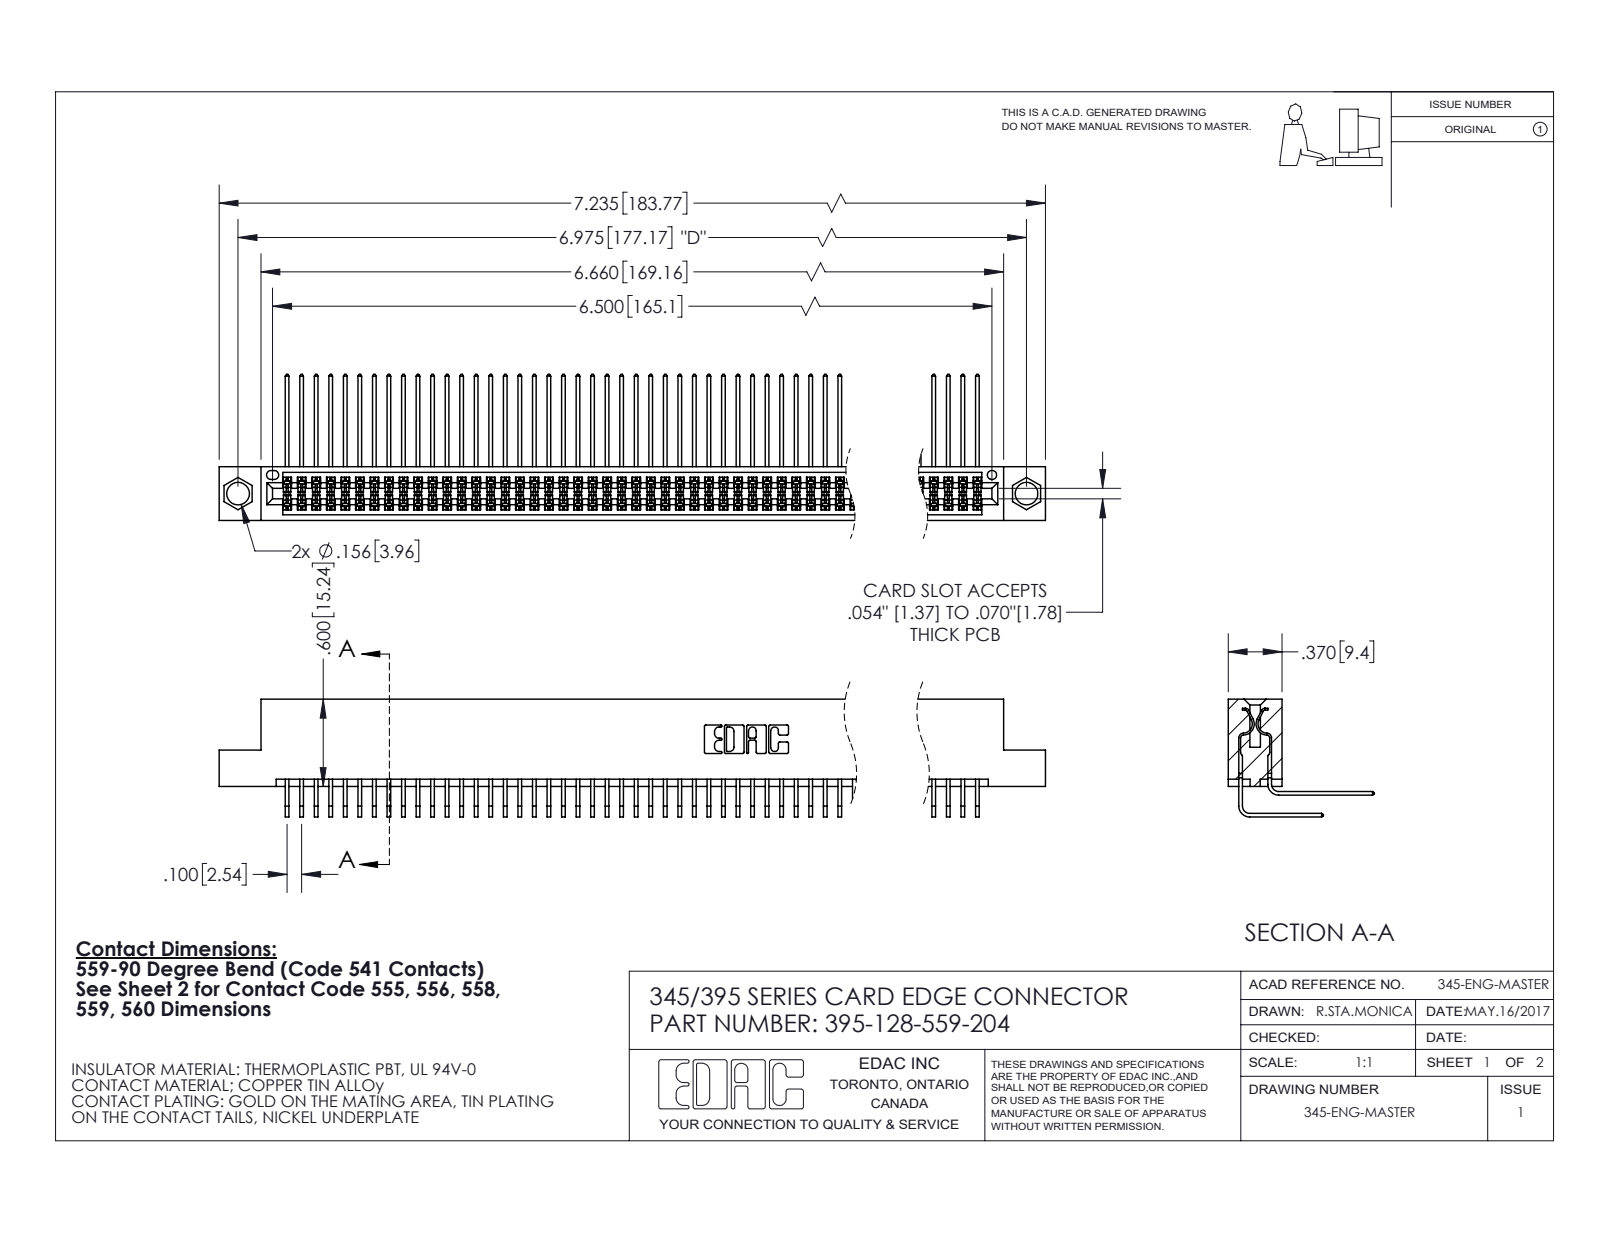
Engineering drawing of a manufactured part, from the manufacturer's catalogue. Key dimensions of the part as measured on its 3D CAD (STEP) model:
Part name (STEP PRODUCT): 345-292-001_559 Tail - 2; 395-128-559-204; 345 Part_Flush Mounting Lugs - 0.156 Dia-TI; 345-292-001_558 559 Tail - 1
STEP written by: SolidWorks 2020 (CONFIG_CONTROL_DESIGN)
Units: inches
Bodies: 129 solids, 6796 faces (4574 planar, 2222 cylindrical, 0 other)
Overall size (bounding box): 7.235 × 1.005 × 0.809
Volume: 1.14 in³ · Surface area: 48.63 in²
Round holes (diameter × count): ⌀0.156 ×2, ⌀0.064 ×1
Partial cylindrical surfaces — rounded edges, fillets, slot ends (radius × count): R0.006 ×193, R0.01 ×22, R0.007 ×6, R0.031 ×6, R0.026 ×3, R0.014 ×2, R0.019 ×2, R0.022 ×2
Main face-to-face distances: 0.072, 0.298, 0.2, 0.37, 0.098, 0.272, 0.025, 0.225, 0.175, 0.15
Hole centre spacings: 0.27, 6.739, 6.975
